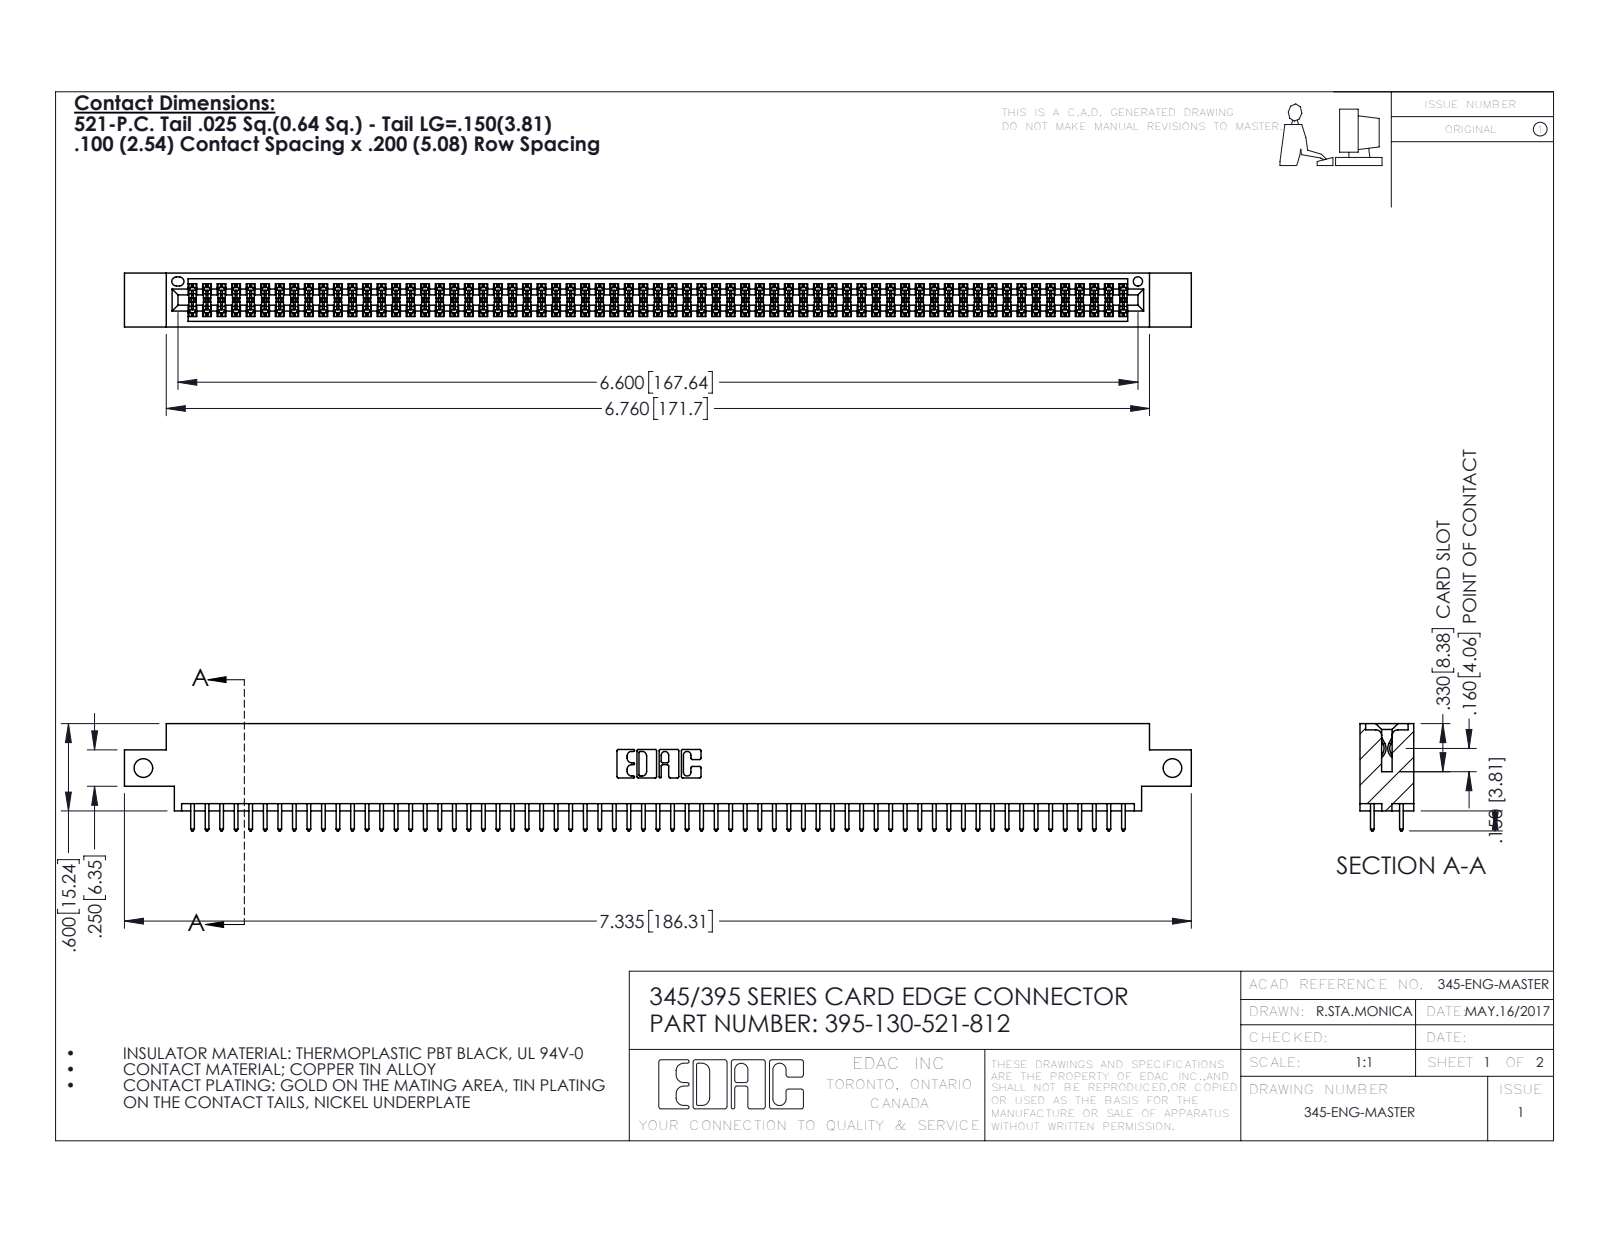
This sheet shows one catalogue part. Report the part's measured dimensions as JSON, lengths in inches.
{"part_name": "395-130-521-812; 345 Part_0.170 Offset - Side Mount; 345-292-001_345-293-121", "step_written_by": "SolidWorks 2016 (CONFIG_CONTROL_DESIGN)", "units": "inches", "bodies": {"solids": 131, "faces": 6630, "planar": 4374, "cylindrical": 2256, "other": 0}, "overall_size": [7.335, 0.737, 0.37], "volume_in3": 1.102, "surface_area_in2": 41.54, "round_holes": [[0.128, 2], [0.064, 1]], "partial_cylinders_radius": [[0.006, 195], [0.01, 130], [0.01, 22], [0.007, 6], [0.031, 6], [0.026, 3], [0.014, 2], [0.019, 2]], "face_to_face_distances": [0.072, 0.298, 0.2, 0.37, 0.098, 0.272, 0.025, 0.225, 0.175, 0.149], "hole_center_spacings": [7.075]}
